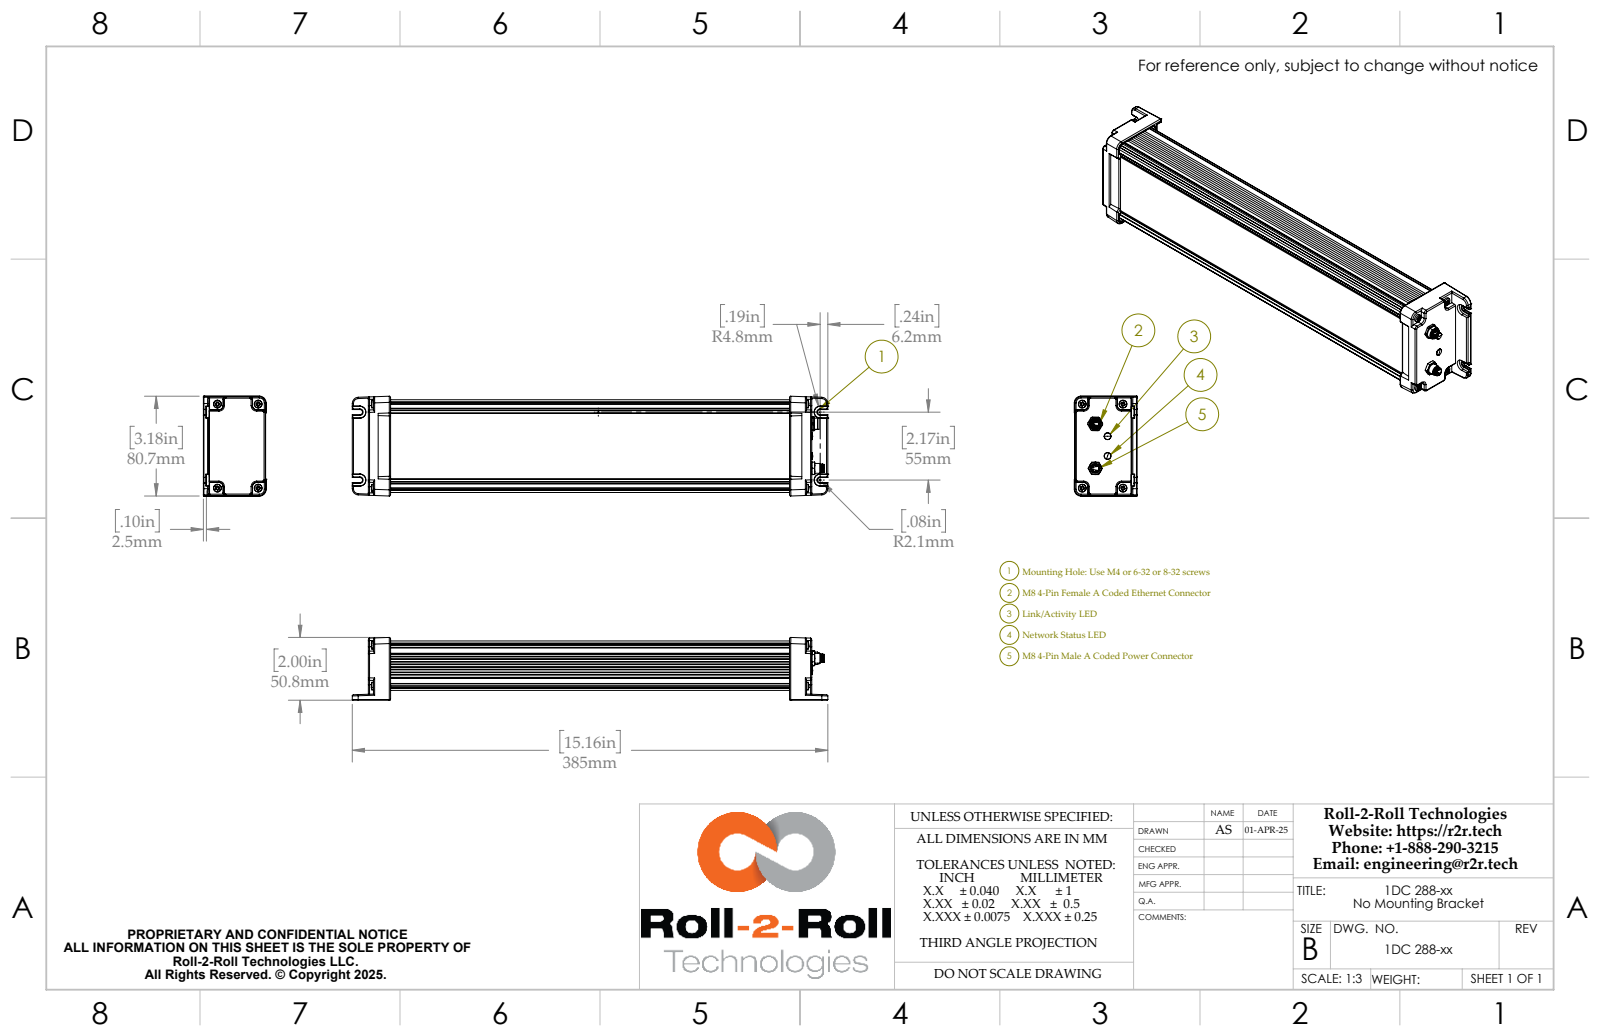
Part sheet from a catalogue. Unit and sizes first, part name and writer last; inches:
Units: inches
Overall size (bounding box): 15.157 × 3.178 × 1.998
Round holes (diameter × count): ⌀0.041 ×2, ⌀0.228 ×1, ⌀0.232 ×1, ⌀0.291 ×1
Round bosses / shafts (diameter × count): ⌀0.118 ×4, ⌀0.098 ×4, ⌀0.043 ×4, ⌀0.039 ×4, ⌀0.031 ×4, ⌀0.191 ×2, ⌀0.354 ×1, ⌀0.35 ×1
Partial cylindrical surfaces — rounded edges, fillets, slot ends (radius × count): R0.02 ×106, R0.039 ×74, R0.079 ×56, R0.012 ×20, R0.035 ×10, R0.197 ×9, R0.044 ×8, R0.047 ×8
Main face-to-face distances: 0.079, 1.299, 1.378, 1.22, 0.167, 0.159, 1.458, 1.379, 0.08, 0.098
Hole centre spacings: 0.07, 0.071, 0.081, 1.417, 1.462, 1.484
Volume: 20.42 in³ · Surface area: 398.9 in²
Bodies: 19 solids, 1475 faces (567 planar, 551 cylindrical, 357 other)
Part name (STEP PRODUCT): 1DC 288-xx
STEP written by: SolidWorks 2017 (CONFIG_CONTROL_DESIGN)
